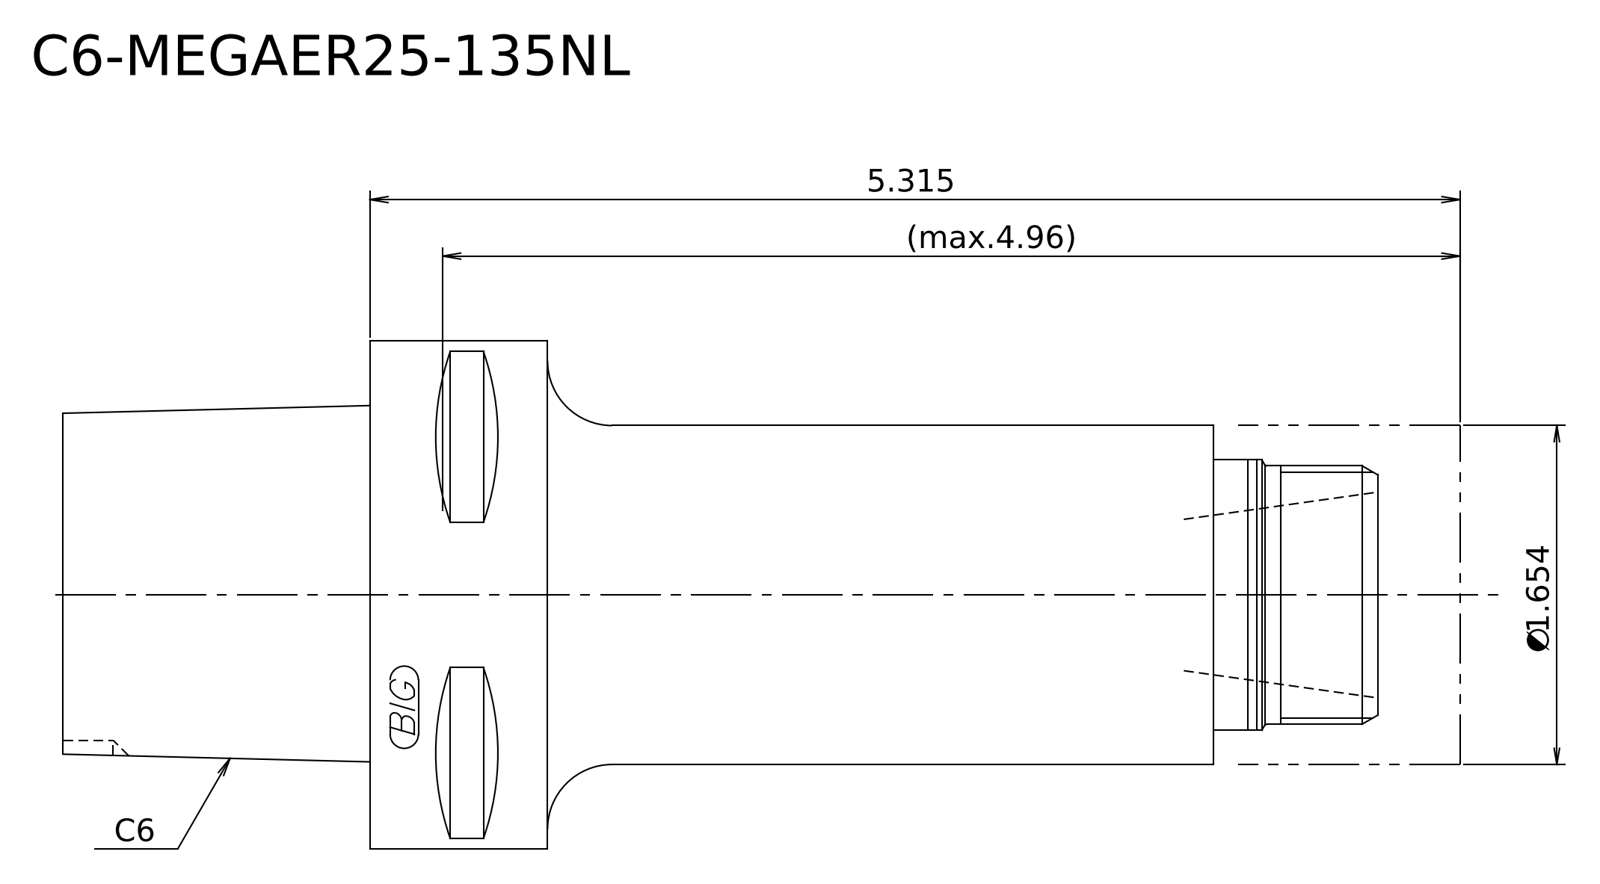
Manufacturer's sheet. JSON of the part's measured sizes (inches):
{"step_written_by": "Kubotek KeyCreator 2011 V10.0.2 (22737) (automotive_design)", "units": "inches", "bodies": {"solids": 2, "faces": 18, "planar": 7, "cylindrical": 5, "other": 6}, "overall_size": [6.811, 2.48, 2.48], "volume_in3": 18.14, "surface_area_in2": 53.2, "round_bosses_or_shafts": [[2.48, 1], [1.654, 1], [1.319, 1], [1.26, 1]], "face_to_face_distances": [4.232, 1.083, 5.315, 6.811, 5.728, 1.496, 0.402, 0.681, 4.913, 6.409]}
